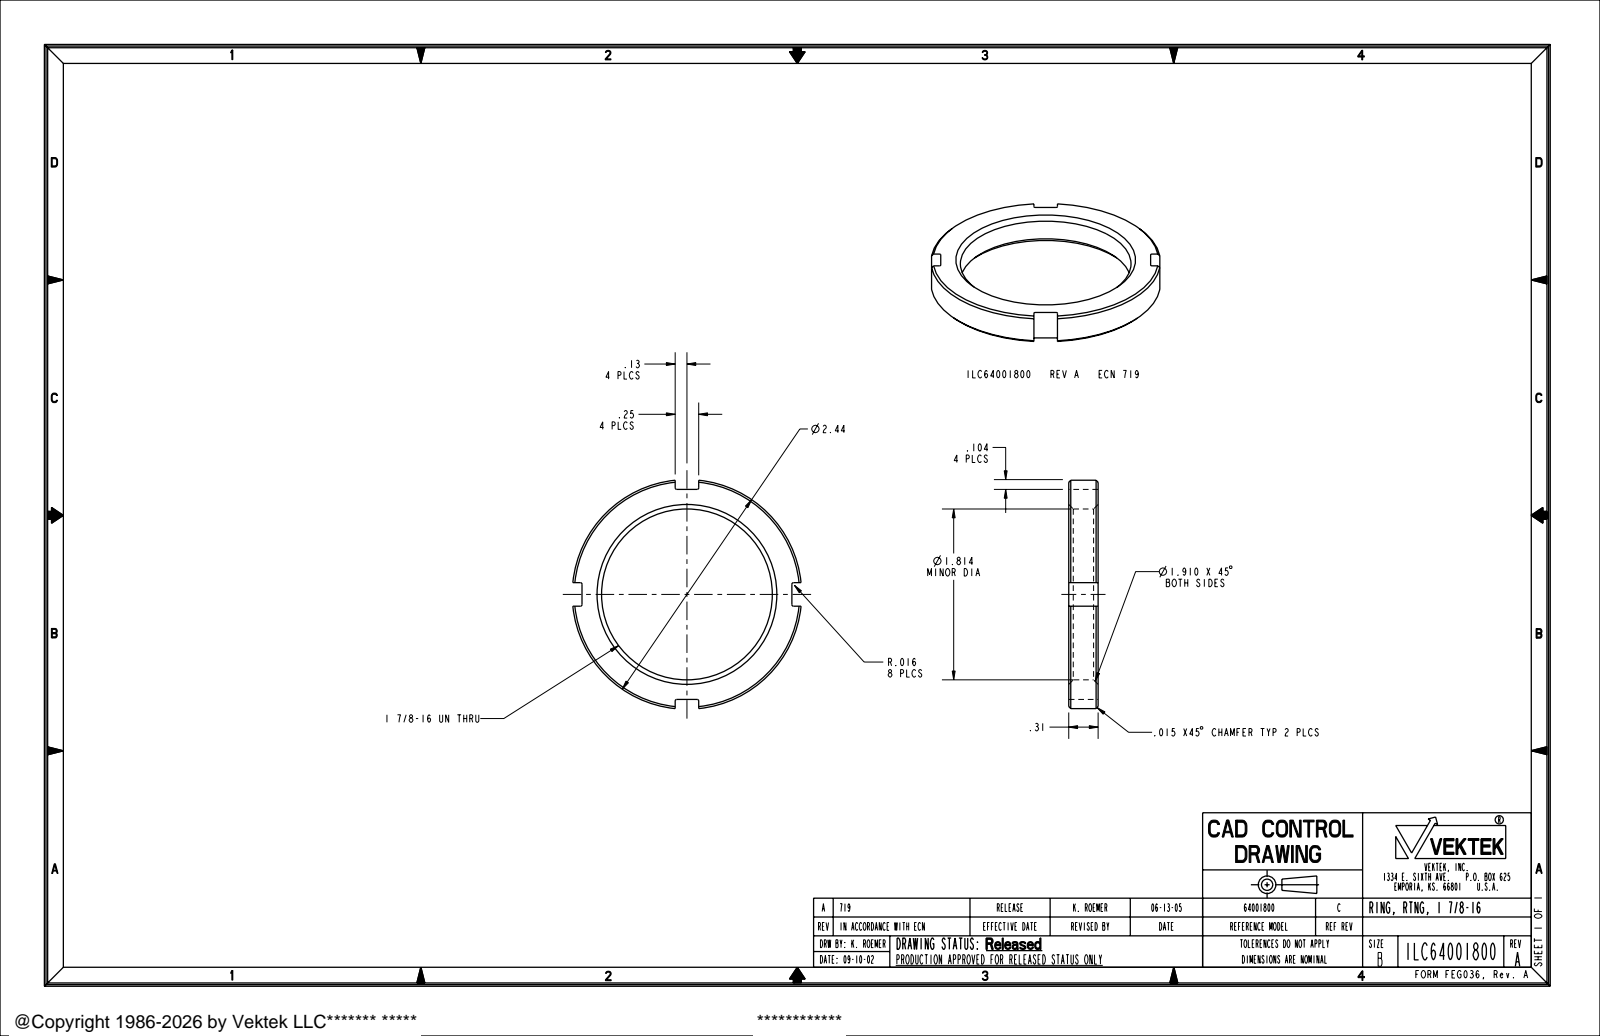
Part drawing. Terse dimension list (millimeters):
name: ILC64001800
written by: PRO/ENGINEER BY PARAMETRIC TECHNOLOGY CORPORATION, 2004290 (AUTOMOTIVE_DESIGN_CC2)
unit: mm
bodies: 1 solid, 40 faces (14 planar, 14 cylindrical, 12 other)
size: 61.9 × 61.9 × 7.9
volume: 9 870 mm³; area: 5 079 mm²
holes: 1× ⌀46.1
bosses: 1× ⌀61.9
rounds: 8× R0.4
face distances: 7.9, 25.1, 31.5, 56.6, 6.4
